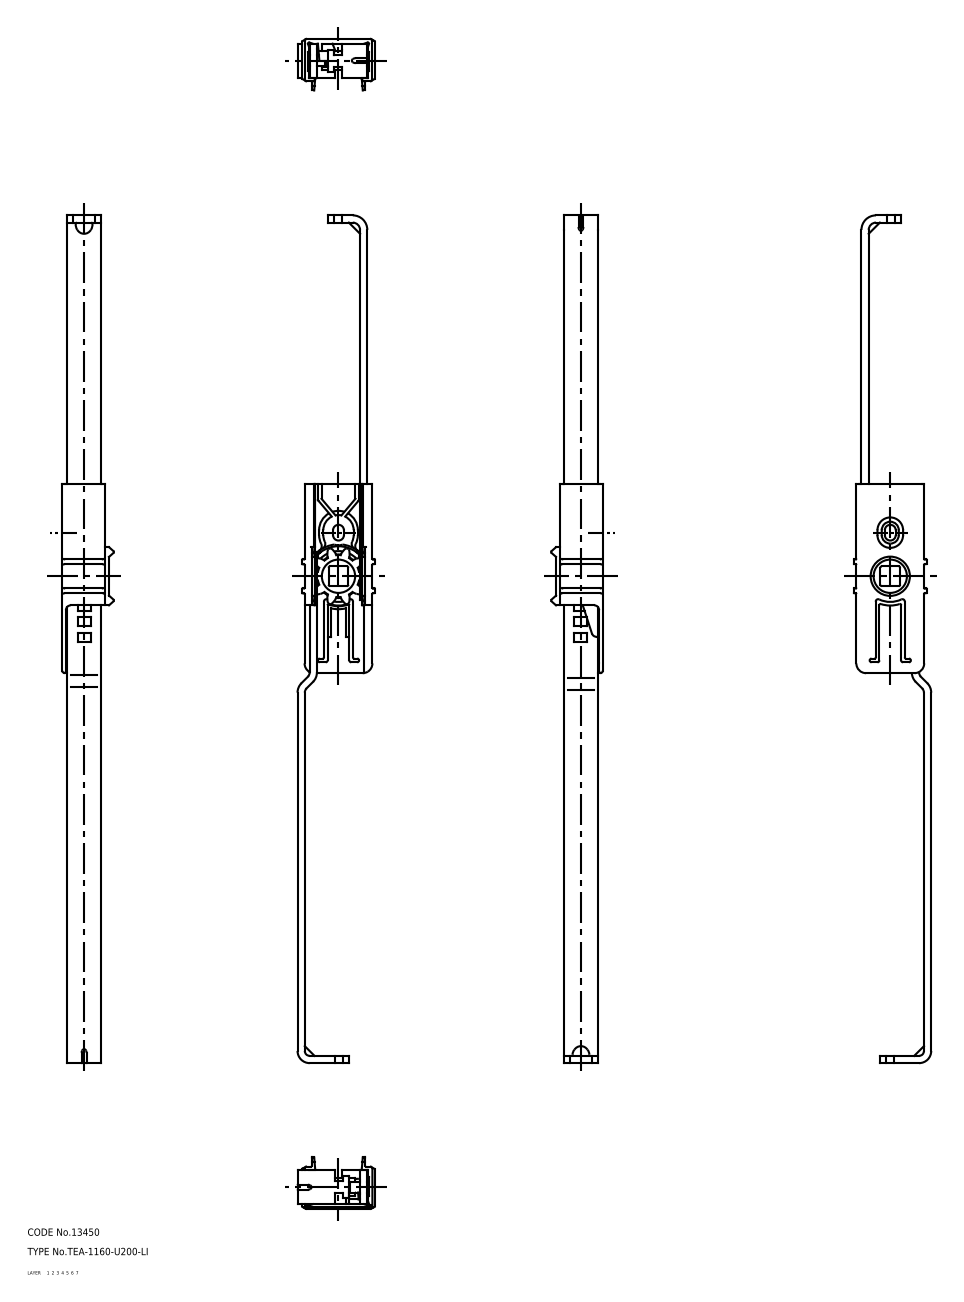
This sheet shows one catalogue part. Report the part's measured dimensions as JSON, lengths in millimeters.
{"part_name": "rod_2_mr; rod_1_mr; body_2_mr; body_1_mr (+1 more)", "step_written_by": "CADfix (AUTOMOTIVE_DESIGN)", "units": "millimeters", "bodies": {"solids": 4, "faces": 433, "planar": 0, "cylindrical": 0, "other": 433}, "overall_size": [350, 31.9, 21.3], "volume_mm3": 24814, "surface_area_mm2": 24740}
